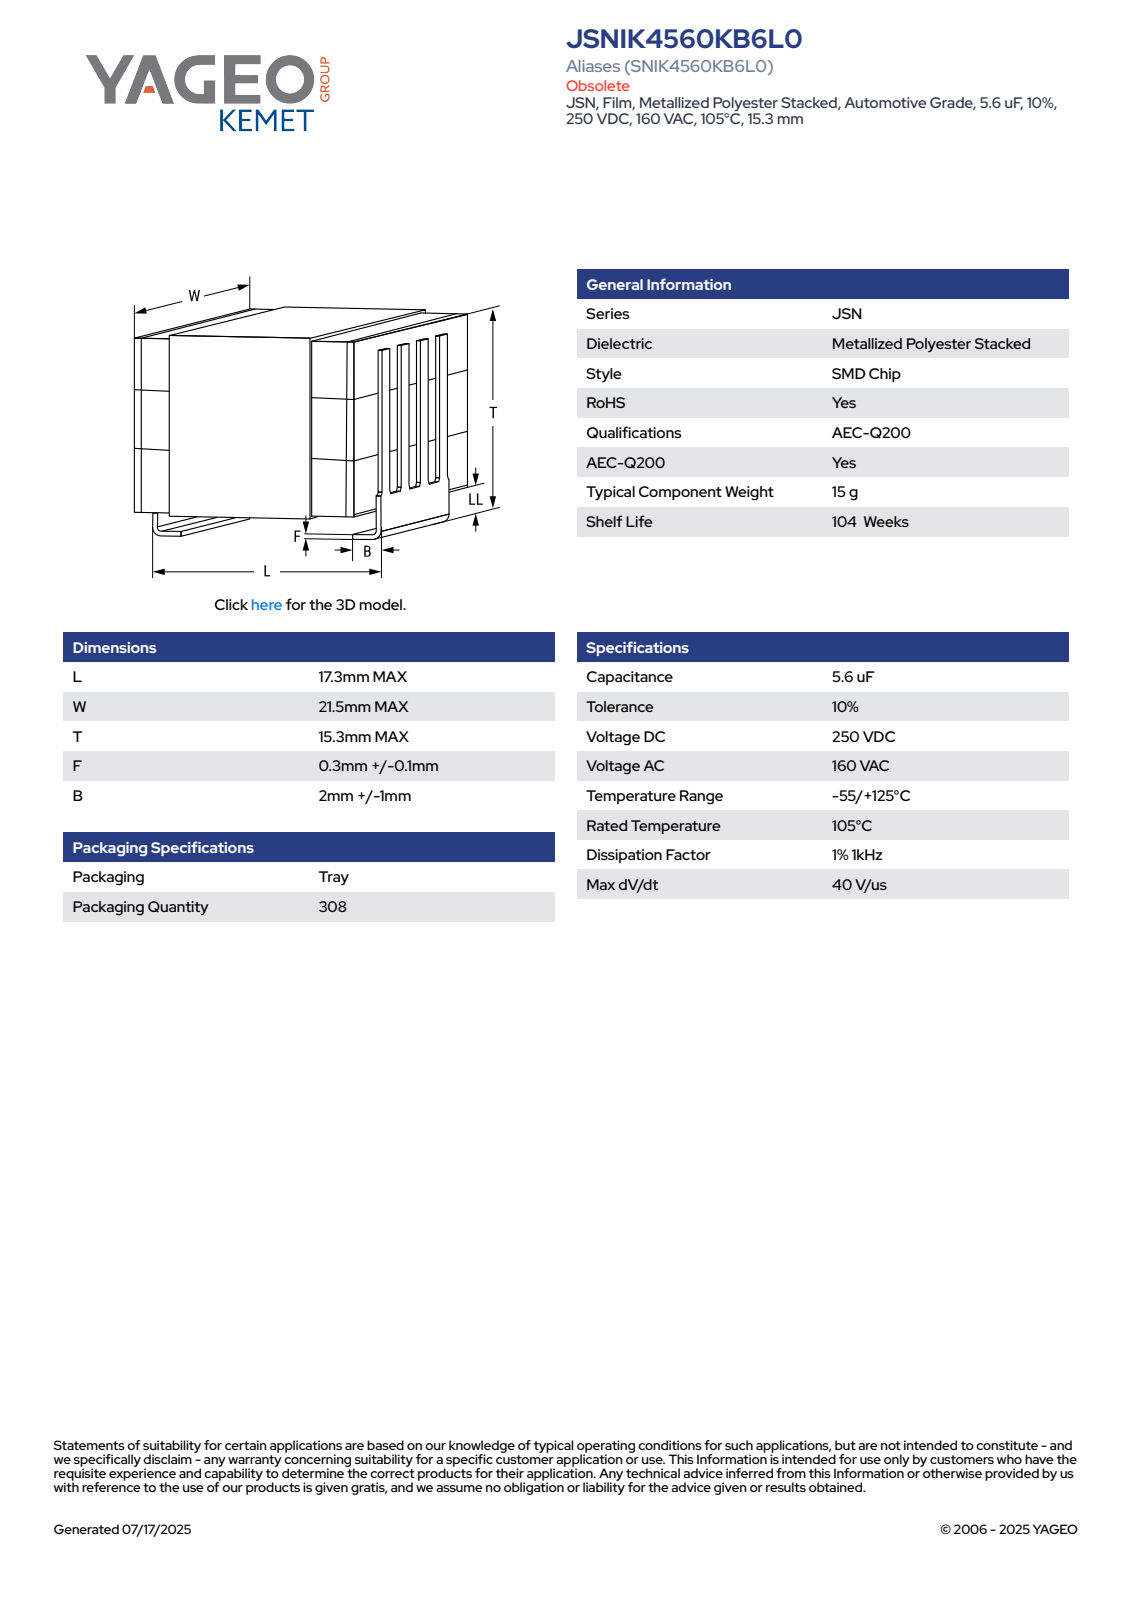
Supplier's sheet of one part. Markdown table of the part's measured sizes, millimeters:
| quantity | value |
| --- | --- |
| part name | CFS_KJSN_L17.3W21.5T15.3F0.40 |
| STEP written by | SolidWorks 2014 (AUTOMOTIVE_DESIGN) |
| units | millimeters |
| bodies | 4 solids, 101 faces (97 planar, 4 cylindrical, 0 other) |
| overall size | 21.5 × 17.3 × 15.3 |
| volume | 4 430 mm³ |
| surface area | 2 891 mm² |
| partial cylindrical surfaces (radius × count) | 0.2 × 4 |
| main face-to-face distances | 4.05, 8.15, 3.95, 8.05, 4.1, 0.4, 16.9, 4.15, 8.25, 12.2 |
